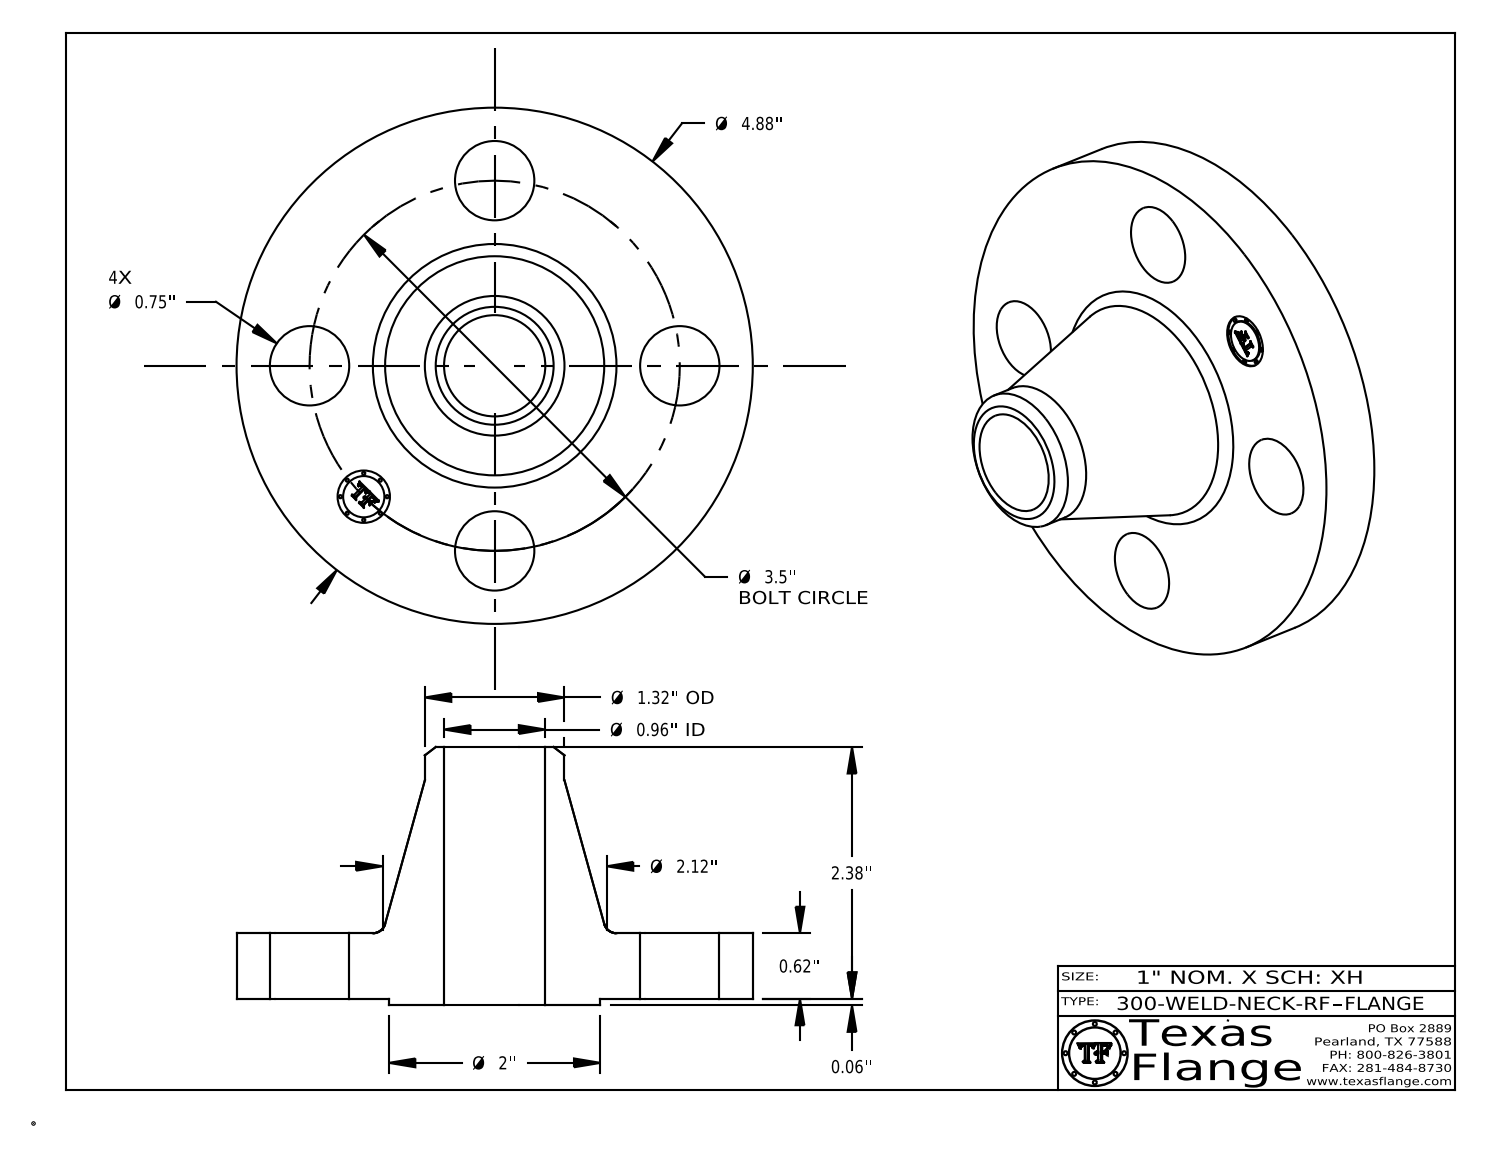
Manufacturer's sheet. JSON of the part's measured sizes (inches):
{"part_name": "300-WELD-NECK-RF", "step_written_by": "CATIA V5 STEP AP214 (AUTOMOTIVE_DESIGN)", "units": "inches", "bodies": {"solids": 1, "faces": 411, "planar": 369, "cylindrical": 36, "other": 6}, "overall_size": [4.88, 4.88, 2.443], "volume_in3": 12.78, "surface_area_in2": 62.46, "round_holes": [[0.75, 4], [0.495, 1], [0.957, 1]], "round_bosses_or_shafts": [[0.03, 8], [4.88, 1], [2, 1], [1.32, 1], [0.39, 1]], "face_to_face_distances": [0.62, 0.063, 0.683, 2.443, 2.38, 1.76, 0.015, 0.668, 0.605, 1.775], "hole_center_spacings": [1.75, 2.475, 1.339, 3.233, 3.5]}
